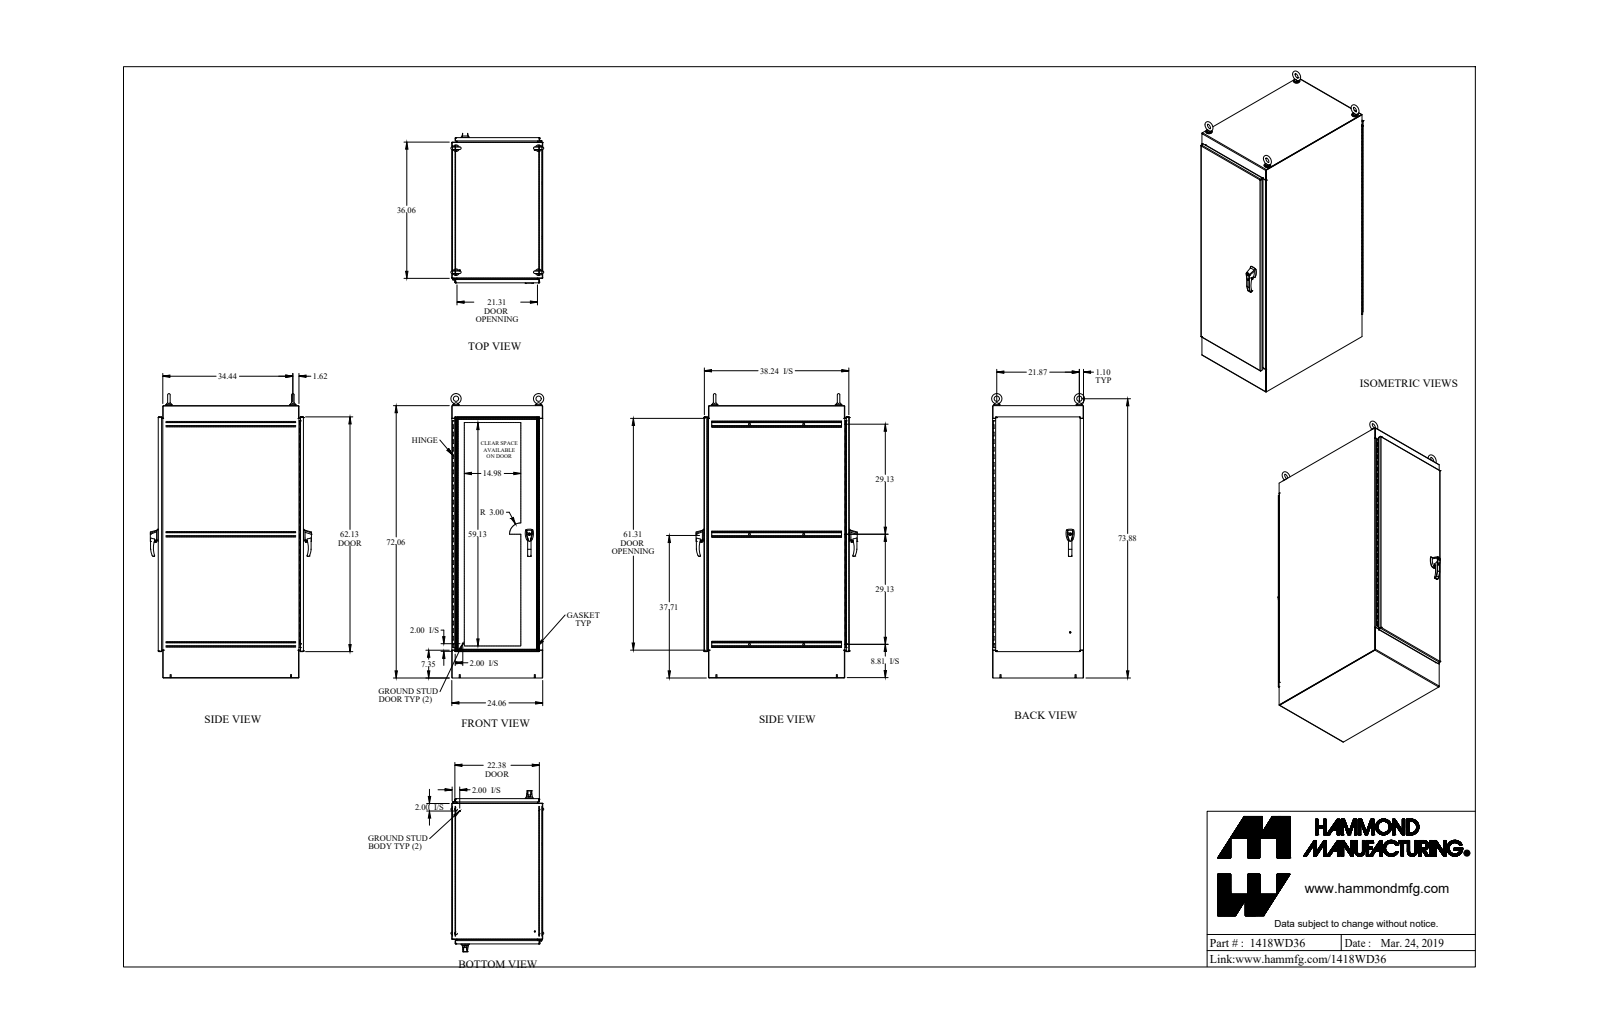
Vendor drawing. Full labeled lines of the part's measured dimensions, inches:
Part name (STEP PRODUCT): 1418WD36_Default
STEP written by: SolidWorks 2019 (CONFIG_CONTROL_DESIGN)
Units: inches
Bodies: 91 solids, 3188 faces (1386 planar, 1476 cylindrical, 326 other)
Overall size (bounding box): 75.713 × 42.664 × 25.118
Volume: 1 279 in³ · Surface area: 26 829 in²
Round holes (diameter × count): ⌀0.304 ×20, ⌀0.5 ×6, ⌀0.25 ×4, ⌀0.257 ×4, ⌀0.28 ×4, ⌀0.281 ×4, ⌀0.313 ×4, ⌀0.39 ×4, ⌀0.413 ×4, ⌀0.527 ×4, ⌀0.625 ×4, ⌀0.687 ×4
Round bosses / shafts (diameter × count): ⌀0.281 ×8, ⌀1.75 ×4, ⌀1.5 ×4, ⌀1.25 ×4, ⌀1 ×4, ⌀0.75 ×4, ⌀0.738 ×4, ⌀0.63 ×4
Partial cylindrical surfaces — rounded edges, fillets, slot ends (radius × count): R0.125 ×44, R0.043 ×42, R0.138 ×36, R0.017 ×32, R0.048 ×24, R0.143 ×24, R0.06 ×16, R0.318 ×14
Main face-to-face distances: 0.095, 23.965, 23.87, 38.339, 24.06, 71.965, 1.187, 37.152, 38.244, 38.434
Hole centre spacings: 6, 23.125, 12, 25.352, 18, 28.683, 24, 32.783
